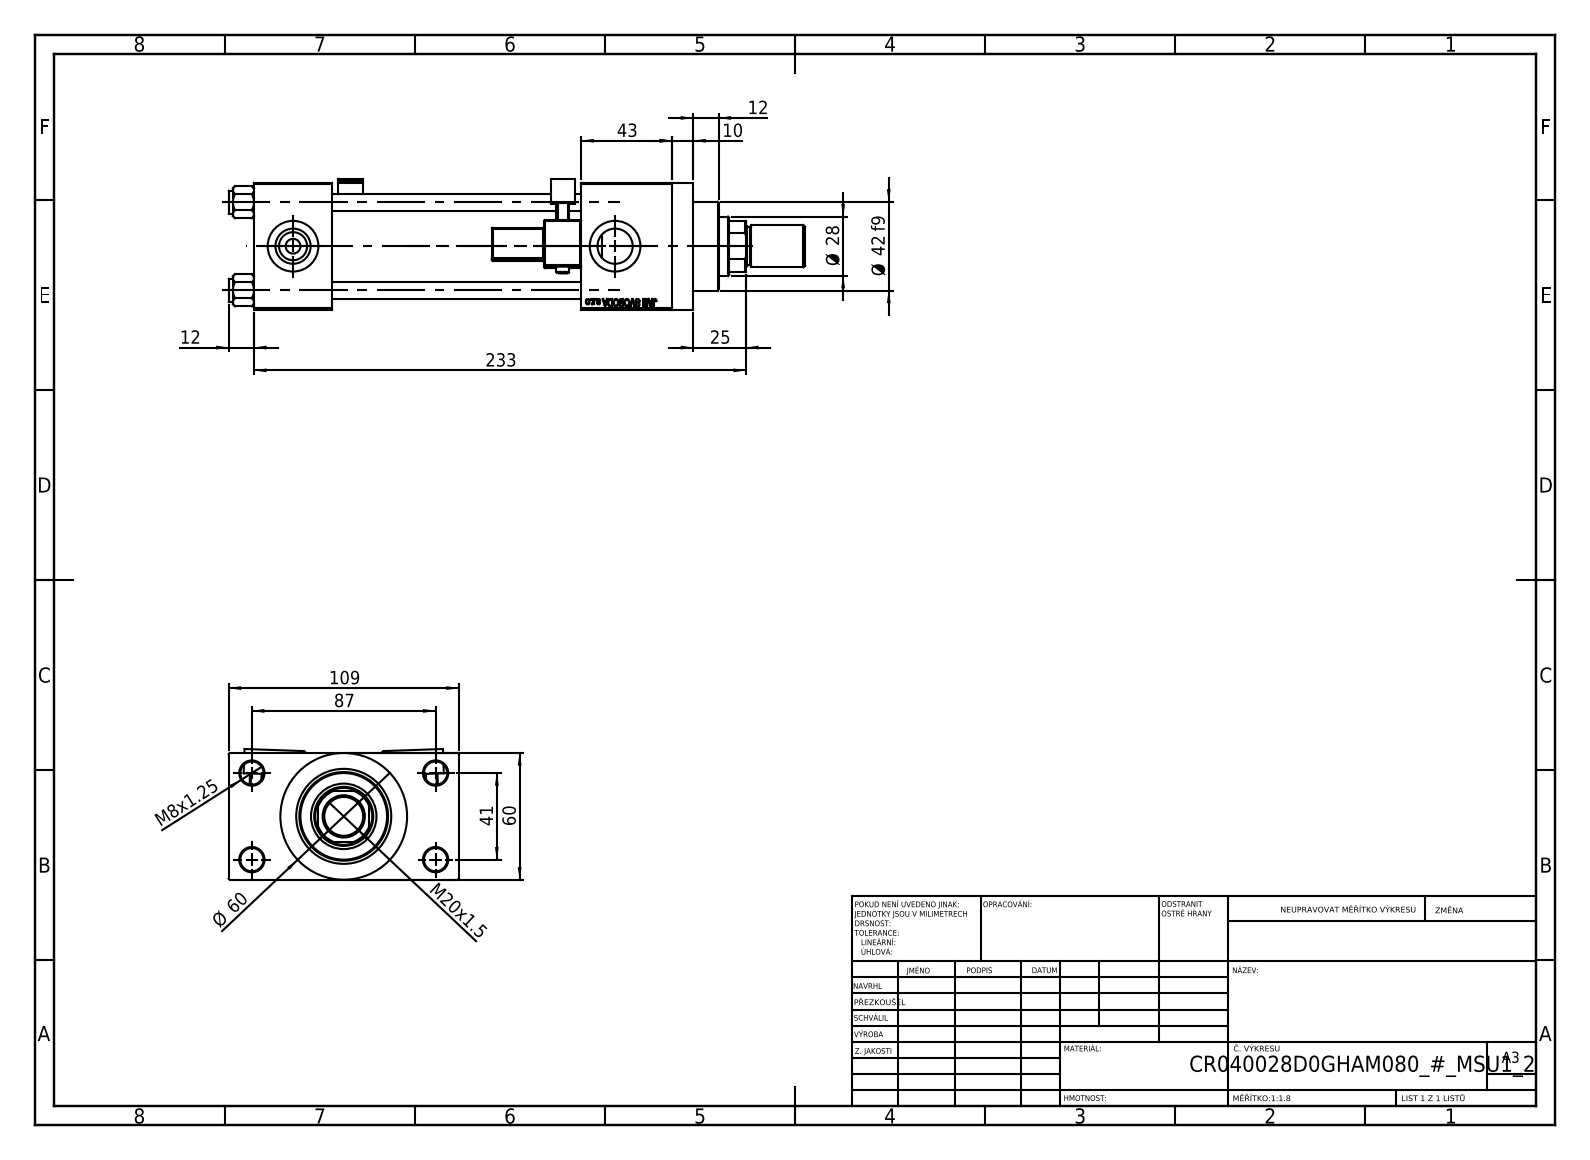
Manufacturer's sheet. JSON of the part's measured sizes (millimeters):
{"part_name": "V215CR_VCP_D; V215CR_D_Body; NUT_M5_D; V215CR_MSU (+3 more)", "step_written_by": "SolidWorks 2019 (CONFIG_CONTROL_DESIGN)", "units": "millimeters", "bodies": {"solids": 14, "faces": 1272, "planar": 560, "cylindrical": 152, "other": 560}, "overall_size": [273, 109, 61.9], "volume_mm3": 651691, "surface_area_mm2": 171147, "round_holes": [[8, 4], [11, 4], [7, 2], [16.66, 2], [24, 2], [18.5, 1], [28, 1], [31, 1], [40, 1], [45, 1]], "round_bosses_or_shafts": [[11, 4], [6, 2], [60, 1], [46, 1], [42, 1], [20, 1], [18, 1]], "partial_cylinders_radius": [[0.5, 48], [1, 2], [2.5, 2], [4, 2], [13.5, 1]], "face_to_face_distances": [60, 118, 24.5, 84.5, 37, 155, 198, 161, 43, 109], "hole_center_spacings": [22.65, 29.49, 41.7, 47.15, 48.09, 64.35, 76.49, 41]}
